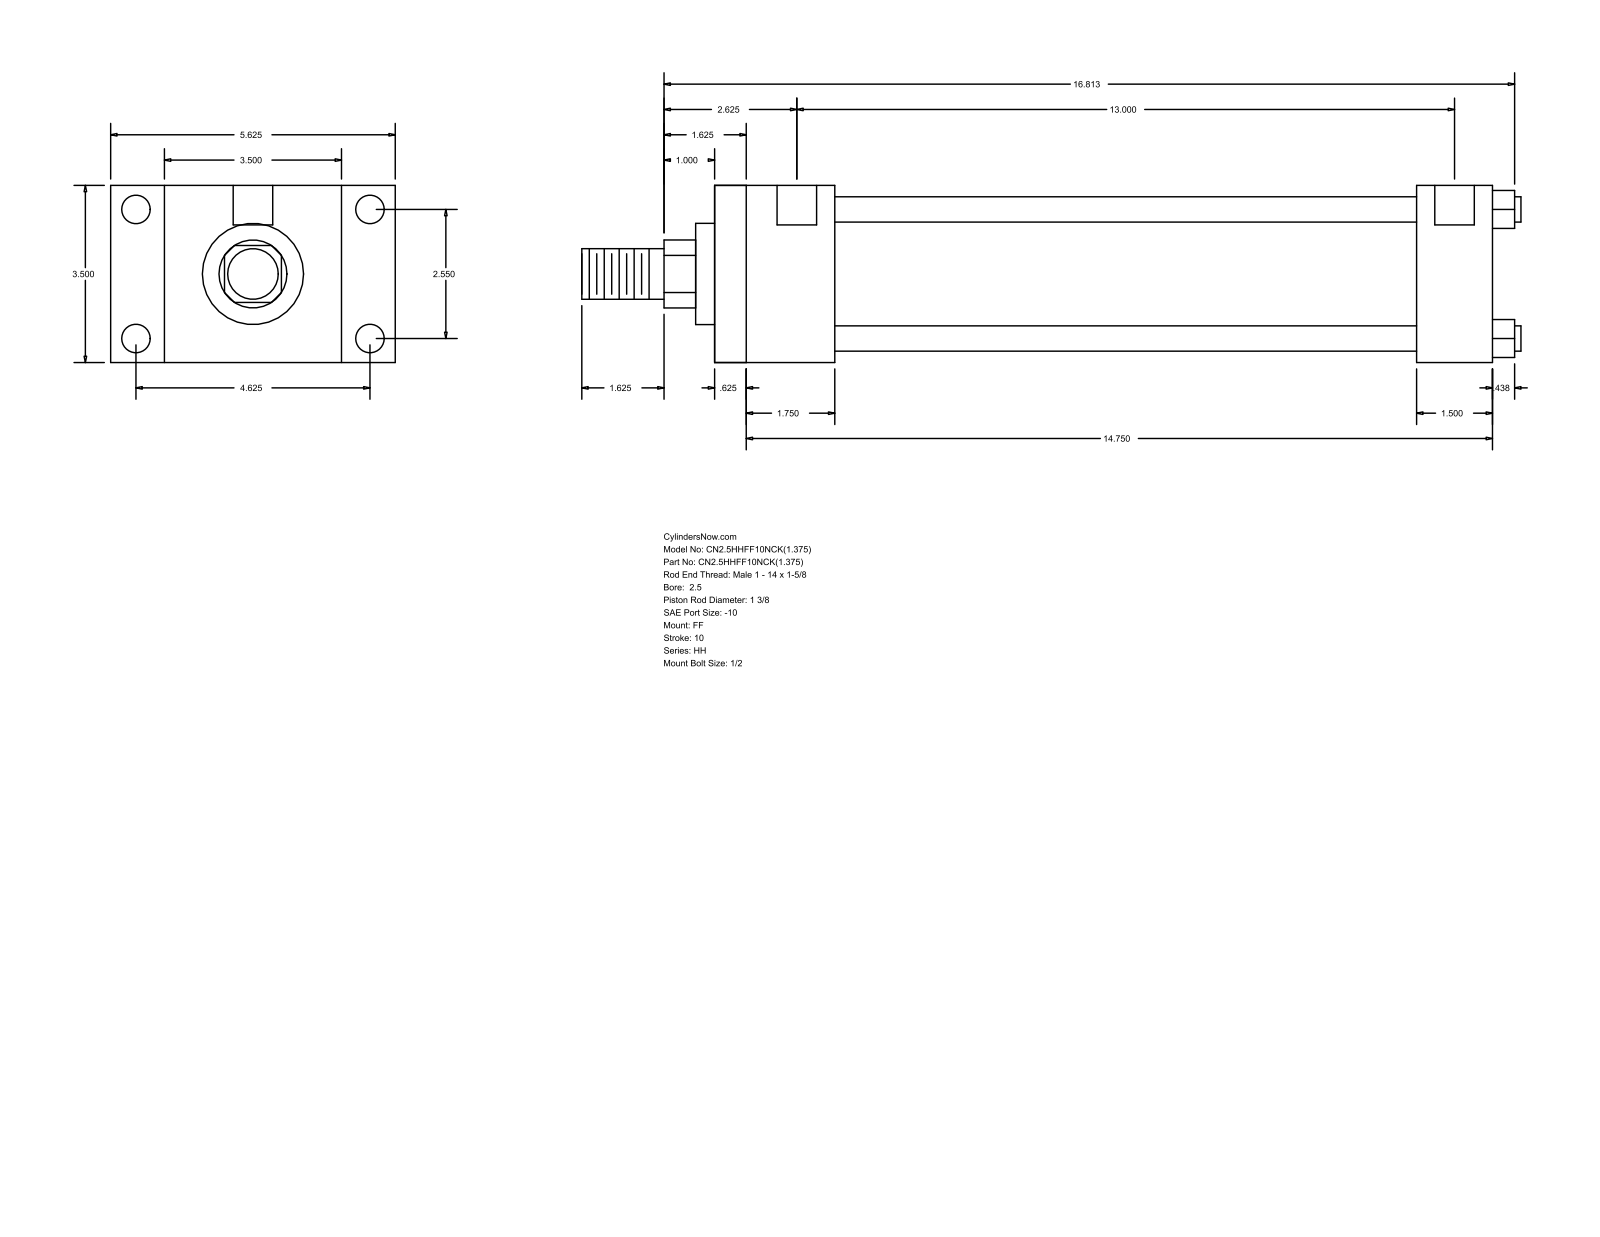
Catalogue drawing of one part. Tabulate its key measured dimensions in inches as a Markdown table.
| quantity | value |
| --- | --- |
| part name | HH_FF__0250_1.375 |
| STEP written by | GSSL Pune (CONFIG_CONTROL_DESIGN) |
| units | inches |
| bodies | 0 solids, 92 faces (64 planar, 28 cylindrical, 0 other) |
| overall size | 18.563 × 5.625 × 3.5 |
| round holes (diameter × count) | 0.219 × 4, 0.563 × 4, 0.781 × 2 |
| round bosses / shafts (diameter × count) | 0.5 × 4, 2.875 × 1, 2 × 1, 1.375 × 1, 1 × 1 |
| partial cylindrical surfaces (radius × count) | 0.672 × 1 |
| main face-to-face distances | 3.5, 15.375, 0.625, 14.75, 2.375, 1.75, 13, 13.875, 13.25, 11.5 |
| hole center spacings | 0.062, 2.55, 4.625, 5.281, 13.063, 13.125, 13 |
